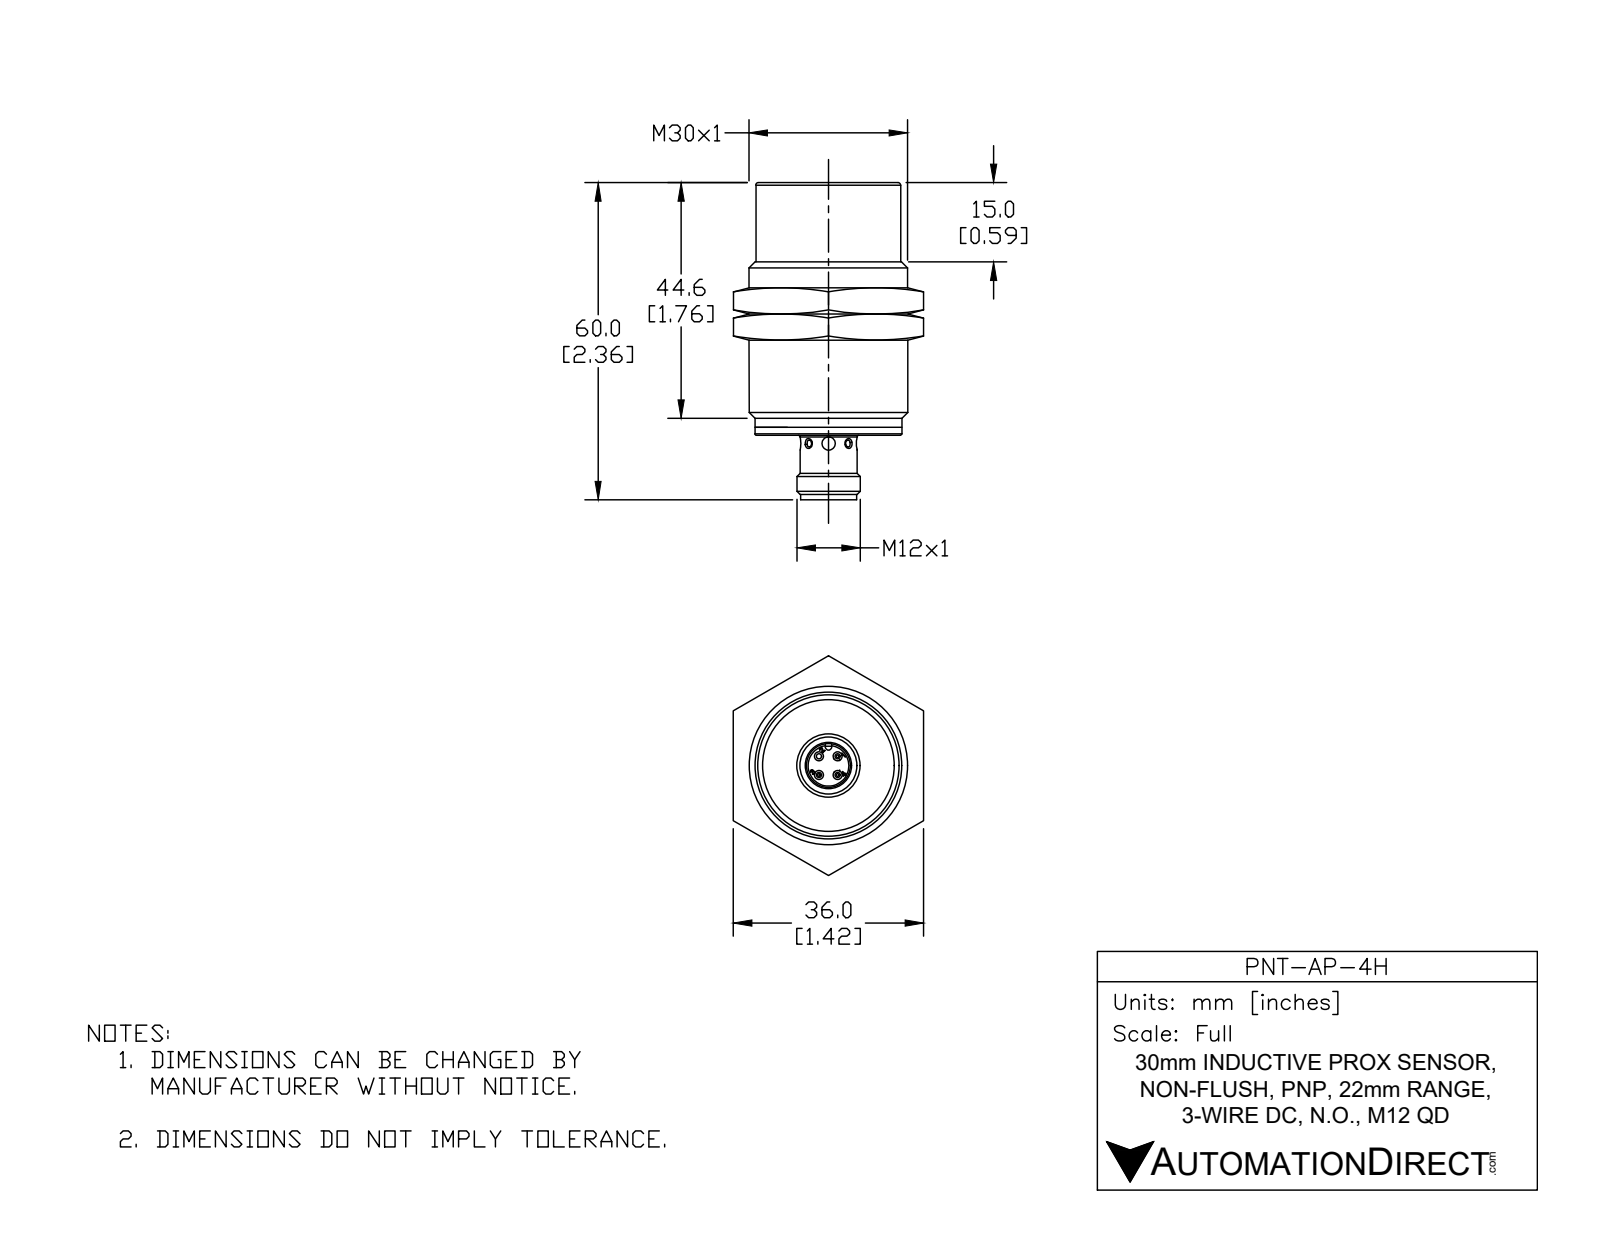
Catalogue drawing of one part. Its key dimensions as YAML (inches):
part_name: "PNT-AP-4H"
step_written_by: "SolidWorks 2017 (AUTOMOTIVE_DESIGN)"
units: inches
bodies: {solids: 1, faces: 660, planar: 260, cylindrical: 164, other: 236}
overall_size: [2.362, 1.181, 1.181]
volume: 1.934
surface_area: 25.17
round_holes:
  - {diameter: 0.043, count: 3}
  - {diameter: 0.04, count: 2}
  - {diameter: 0.098, count: 2}
  - {diameter: 0.038, count: 1}
  - {diameter: 0.04, count: 1}
  - {diameter: 0.323, count: 1}
  - {diameter: 0.327, count: 1}
  - {diameter: 0.394, count: 1}
  - {diameter: 1.047, count: 1}
  - {diameter: 1.076, count: 1}
round_bosses_or_shafts:
  - {diameter: 0.039, count: 9}
  - {diameter: 1.181, count: 1}
  - {diameter: 1.094, count: 1}
  - {diameter: 1.083, count: 1}
  - {diameter: 1.074, count: 1}
  - {diameter: 1.044, count: 1}
  - {diameter: 1.037, count: 1}
  - {diameter: 1.021, count: 1}
partial_cylinders:
  - {radius: 0.004, count: 12}
  - {radius: 0.02, count: 8}
  - {radius: 0.157, count: 6}
  - {radius: 0.03, count: 3}
  - {radius: 0.039, count: 3}
  - {radius: 0.024, count: 1}
  - {radius: 0.031, count: 1}
face_to_face_distances: [0.157, 1.882, 1.724, 0.037, 0.12, 1.844, 1.854, 0.13, 0.031, 0.028]
hole_center_spacings: [0.098, 0.139, 0.197]
